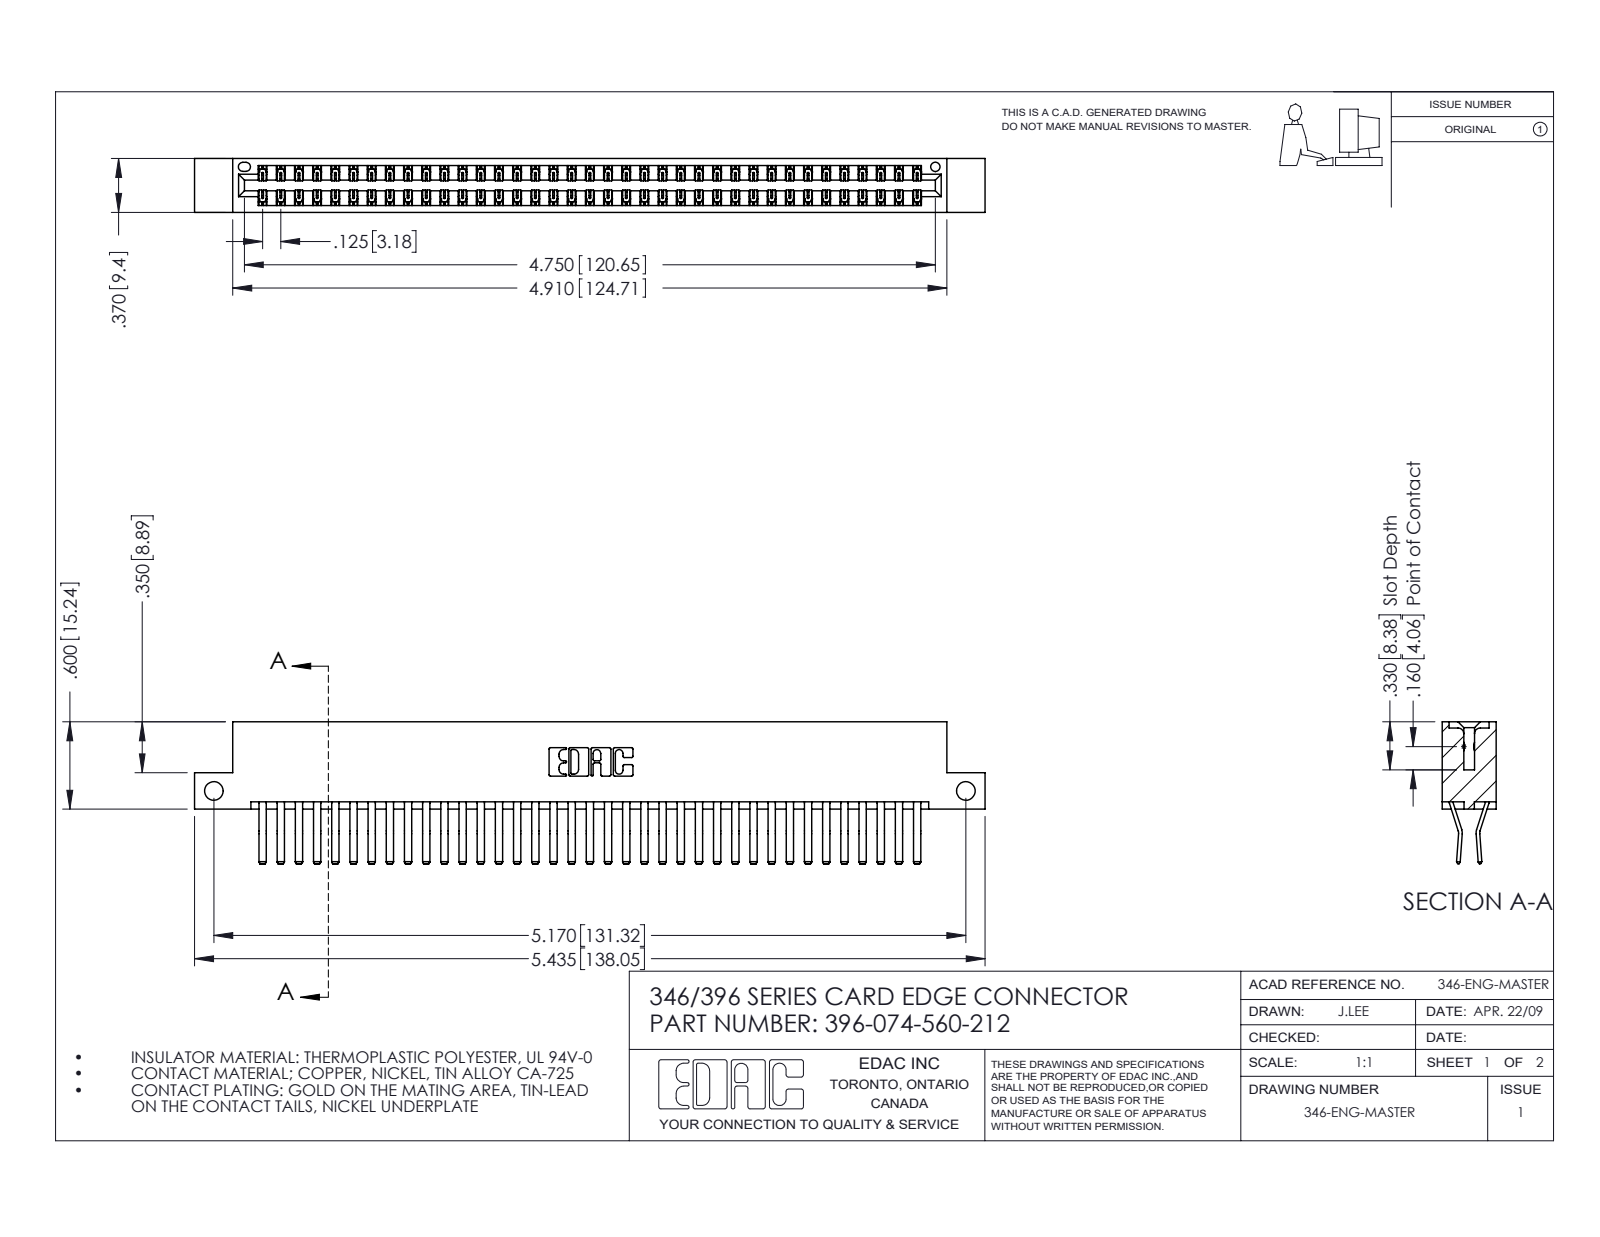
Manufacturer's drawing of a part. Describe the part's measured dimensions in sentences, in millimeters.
The part is named "396-074-560-212; 346 Part_Flush Mounting Lugs - Side Mount; 345-292-001_560 Tail". Its 3-D file was written by "SolidWorks 2016 (CONFIG_CONTROL_DESIGN)". It is 75 solids with 4118 faces: 2666 planar, 1452 cylindrical and 0 other. Overall it measures 138 by 24.8 by 9.4 millimeters. Its volume is 13 800 cubic millimeters and its surface area 20 080 square millimeters. Round holes: 2 of diameter 3.3, 1 of diameter 1.6. Partial cylindrical surfaces (rounded edges, fillets, slot ends): 111 of radius 0.2, 22 of radius 0.3, 6 of radius 0.2, 6 of radius 0.8, 3 of radius 0.7, 2 of radius 0.3, 2 of radius 0.4, 2 of radius 0.6. The main face-to-face distances are 1.2, 8.2, 9.4, 0.6, 6.4, 1.8, 7.6, 7, 3.8, 5.6. The hole center spacings are 131.3.
